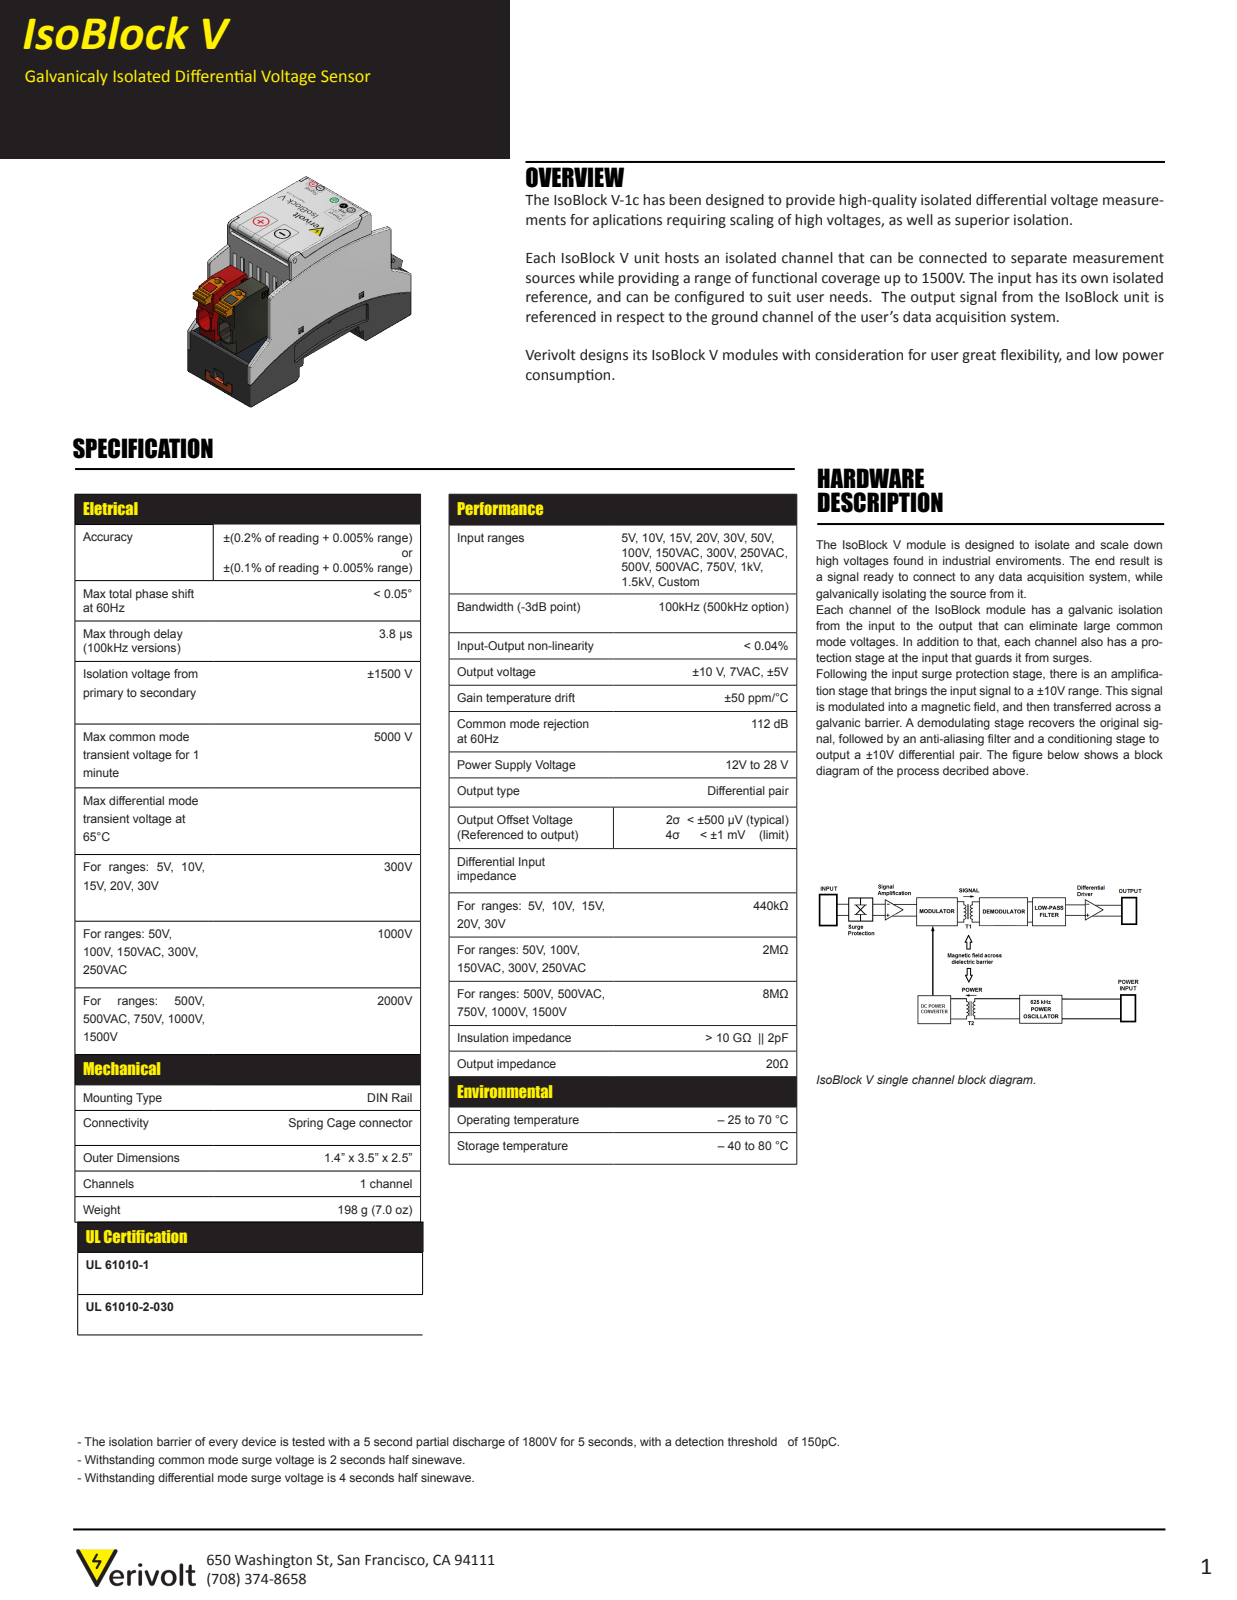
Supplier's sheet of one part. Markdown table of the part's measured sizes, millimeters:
| quantity | value |
| --- | --- |
| part name | IsoBlock V-1c+Shield; BC 2TE V; 2896254; BC_35.6_GEH-UT_HBUS_H.Select (+5 more) |
| STEP written by | Autodesk Inventor 2018 (AUTOMOTIVE_DESIGN) |
| units | millimeters |
| bodies | 35 solids, 3340 faces (2475 planar, 760 cylindrical, 105 other) |
| overall size | 92.3 × 60.7 × 35.6 |
| volume | 49 010 mm³ |
| surface area | 70 970 mm² |
| round holes (diameter × count) | 0.4 × 34, 0.3 × 21, 1 × 18, 0.5 × 15, 0.8 × 10, 0.8 × 10, 1.1 × 10, 1.1 × 8, 0.4 × 7, 1.8 × 4, 2.4 × 4, 0.8 × 3 |
| round bosses / shafts (diameter × count) | 1.4 × 1, 0.5 × 1 |
| partial cylindrical surfaces (radius × count) | 0.5 × 79, 0.2 × 10, 0.2 × 10, 1.2 × 10, 0.5 × 9, 0.4 × 7, 0.3 × 6, 1 × 6 |
| main face-to-face distances | 1.2, 33.1, 1.5, 1.8, 34.3, 35.6, 33.8, 0.6, 32.5, 2.5 |
| hole center spacings | 2.5, 3.6, 5.1, 5.7, 7.6, 8, 10.2, 10.5 |
